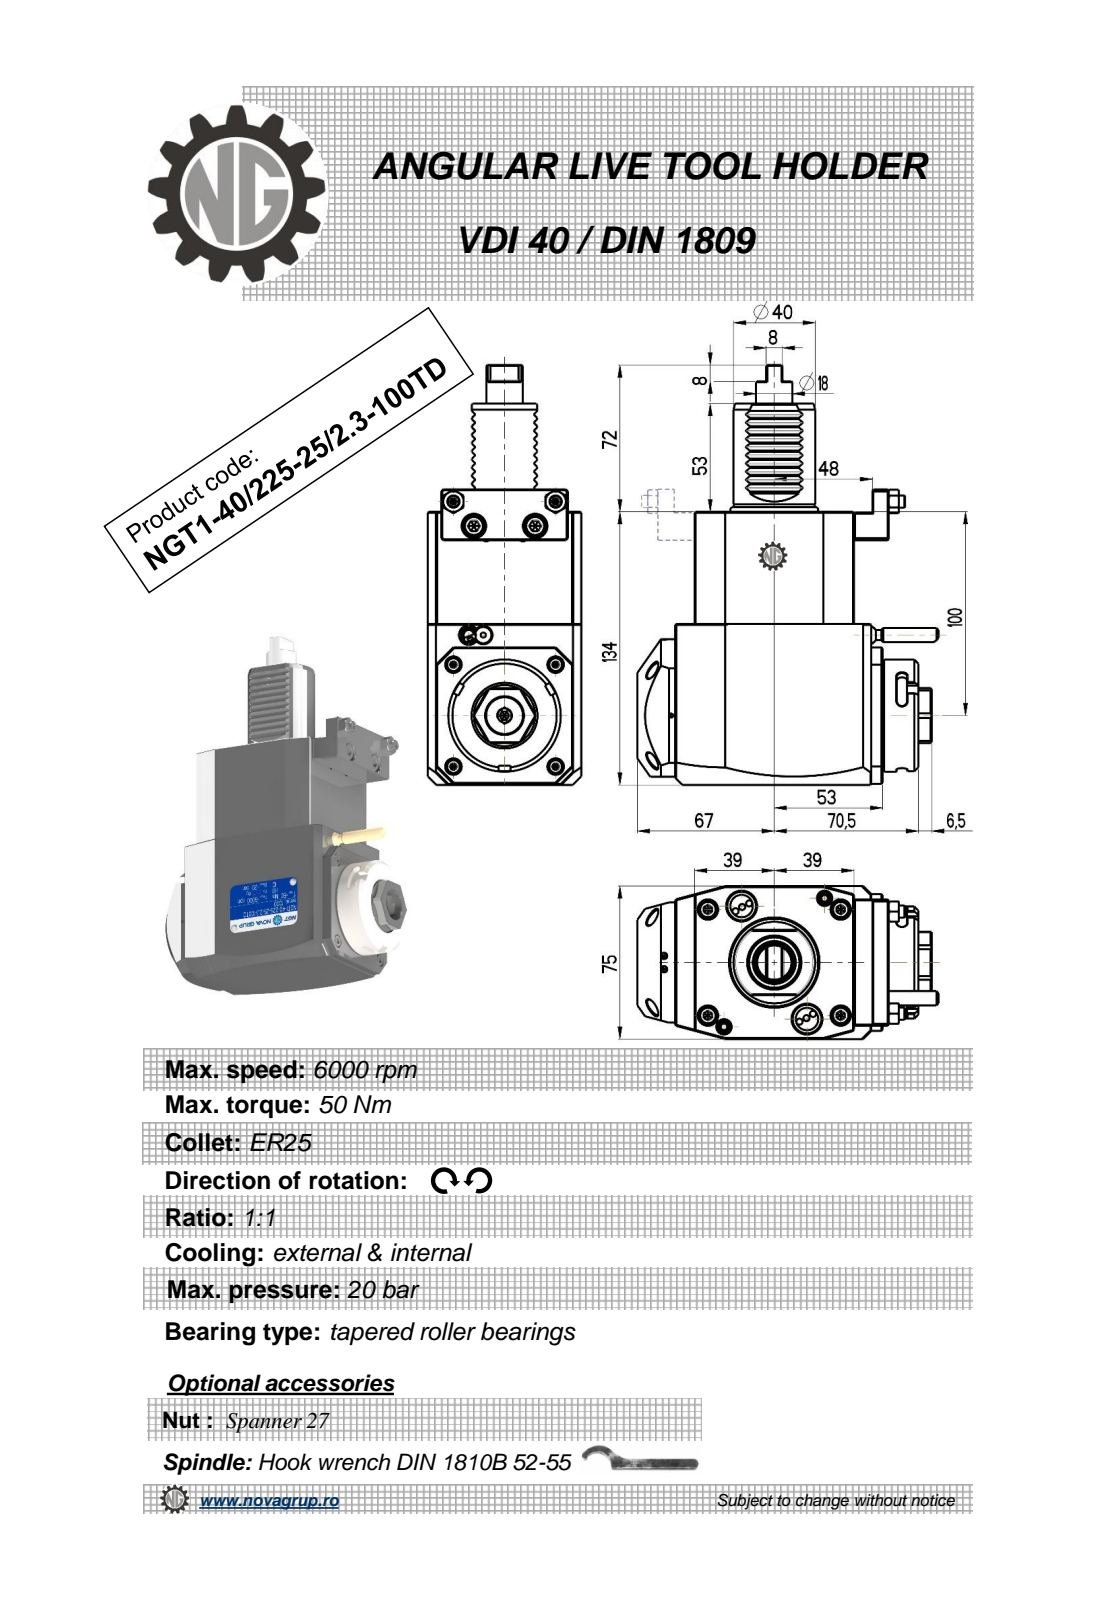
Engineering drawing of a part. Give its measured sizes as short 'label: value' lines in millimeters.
name: NGT1_40_225_25_1_3_100TD
written by: PRO/ENGINEER BY PARAMETRIC TECHNOLOGY CORPORATION, 2010280 (CONFIG_CONTROL_DESIGN)
unit: mm
bodies: 1 solid, 380 faces (213 planar, 77 cylindrical, 90 other)
size: 206 × 147.33 × 75
volume: 1 071 000 mm³; area: 77 693 mm²
holes: 1× ⌀2.5, 1× ⌀3, 1× ⌀18
bosses: 2× ⌀6, 1× ⌀55, 1× ⌀48, 1× ⌀40, 1× ⌀17.8, 1× ⌀8, 1× ⌀7, 1× ⌀5
rounds: 20× R0.3, 10× R0.31, 6× R2.5, 2× R0.8, 2× R180, 1× R15, 1× R24.5, 1× R37.5
face distances: 75, 134, 14, 78, 92, 0.5, 120, 17.5, 17, 14.5
hole spacings: 43.2
